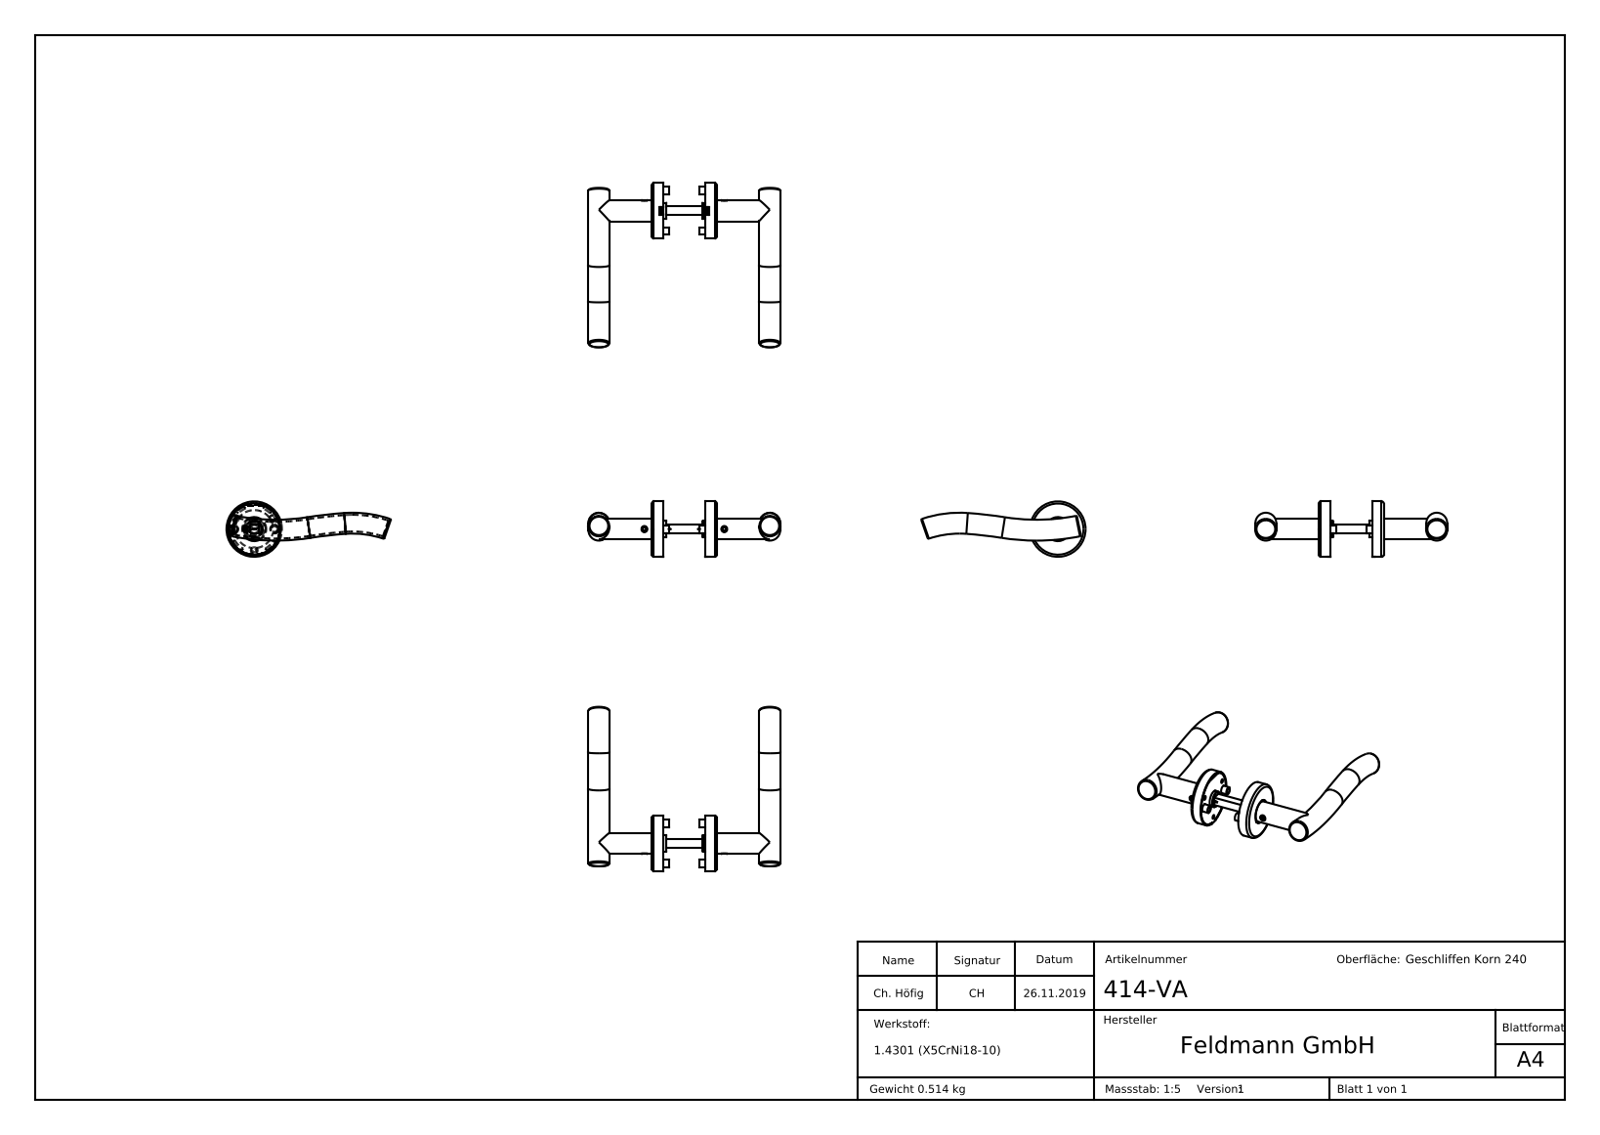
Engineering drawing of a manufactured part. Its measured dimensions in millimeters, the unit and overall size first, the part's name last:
Units: millimetres
Overall size (bounding box): 70000 × 5999.86 × 5999.7
Round holes (diameter × count): ⌀3.7 ×3, ⌀5 ×3, ⌀6.1 ×3, ⌀5.5 ×2, ⌀7.3 ×2, ⌀8 ×2, ⌀15.4 ×1, ⌀15.7 ×1, ⌀16.2 ×1, ⌀22.6 ×1
Round bosses / shafts (diameter × count): ⌀7.1 ×2, ⌀6 ×2, ⌀52 ×1, ⌀50 ×1, ⌀49.8 ×1, ⌀21.4 ×1, ⌀19.6 ×1, ⌀15.2 ×1
Partial cylindrical surfaces — rounded edges, fillets, slot ends (radius × count): R1 ×4, R4.5 ×1, R17.85 ×1, R21 ×1, R23 ×1
Main face-to-face distances: 1, 60, 10.5, 50.5, 9.5, 49.5, 8.1, 40, 0.8, 8
Hole centre spacings: 20, 34.64, 10.14, 19, 27.59, 37.67, 30, 38
Volume: 114 751 mm³ · Surface area: 105 038 mm²
Bodies: 13 solids, 879 faces (539 planar, 118 cylindrical, 222 other)
Part name (STEP PRODUCT): 4XX-VA Teil3; 4XX-VA Teil3_4XX-VA Teil3; DIN914_DIN 914 M6x6; 4XX-VA Teil1_414-VA Teil1 (+8 more)
STEP written by: SolidWorks 2015 (CONFIG_CONTROL_DESIGN)
